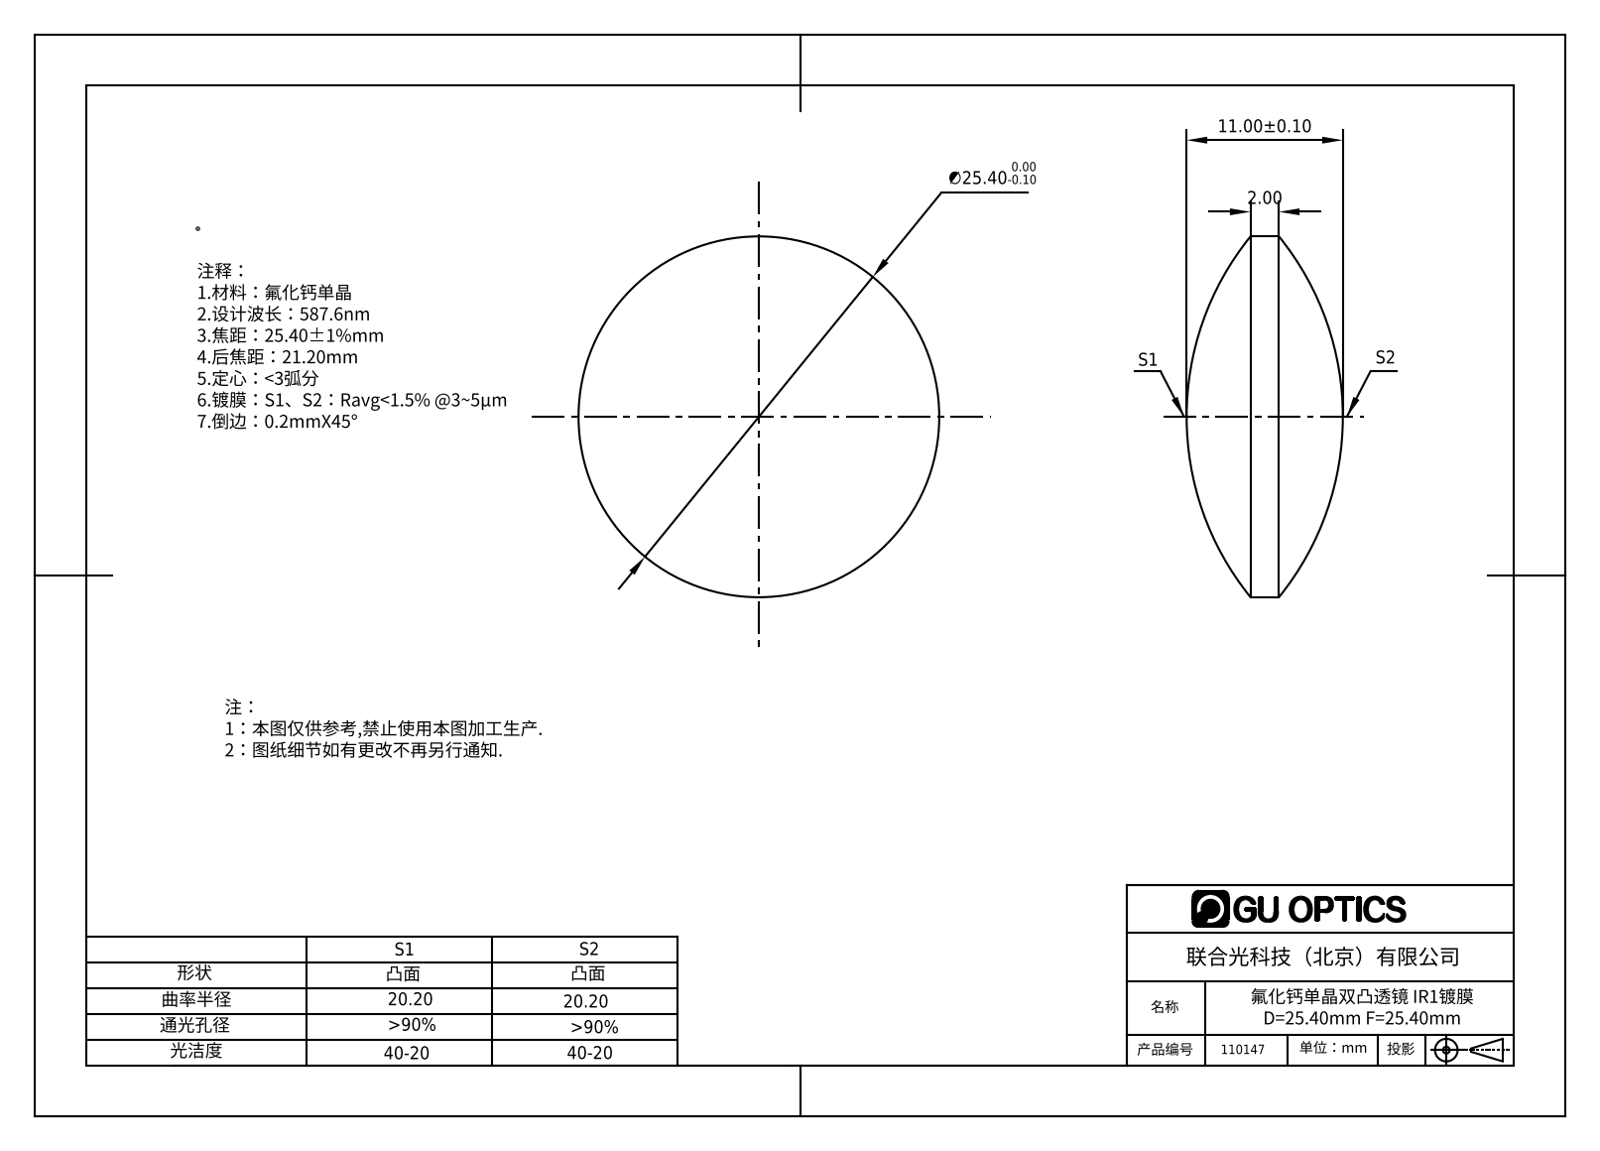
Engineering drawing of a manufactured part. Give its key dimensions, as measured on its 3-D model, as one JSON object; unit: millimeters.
{"part_name": "110139", "step_written_by": "SolidWorks 2016 (CONFIG_CONTROL_DESIGN)", "units": "millimeters", "bodies": {"solids": 1, "faces": 6, "planar": 0, "cylindrical": 2, "other": 4}, "overall_size": [25.4, 25.4, 11], "volume_mm3": 3389, "surface_area_mm2": 1300, "round_bosses_or_shafts": [[25.4, 1]]}
